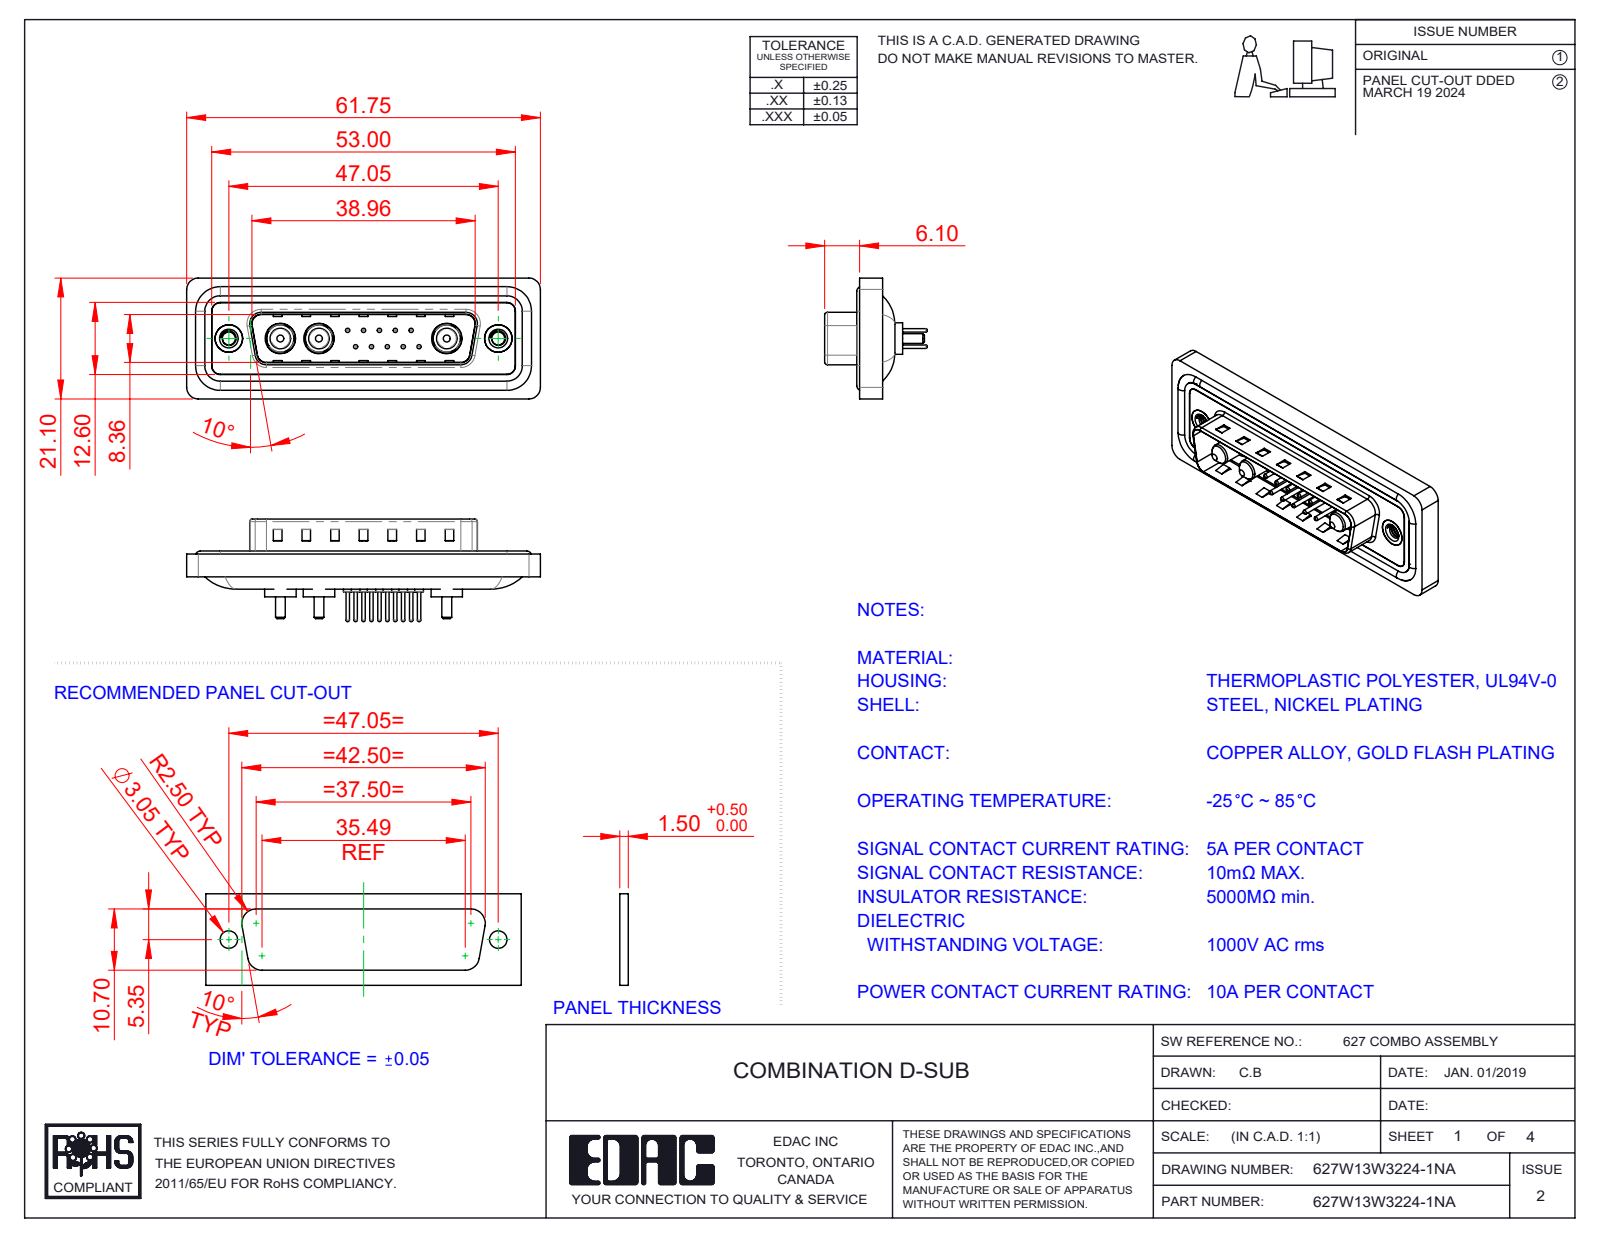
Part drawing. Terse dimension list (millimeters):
name: 627W13W3224-1NA; 627Combo Contact Row 1_24; 627Combo Shell Rear_25 Contacts; 627Combo Contact Row 2_24 (+5 more)
written by: SolidWorks 2023 (CONFIG_CONTROL_DESIGN)
unit: mm
bodies: 23 solids, 968 faces (309 planar, 387 cylindrical, 272 other)
size: 61.75 × 21.1 × 17.9
volume: 7 293 mm³; area: 11 834 mm²
holes: 10× ⌀0.75, 10× ⌀1.6, 10× ⌀2, 3× ⌀4.85, 3× ⌀5.3, 2× ⌀2.26, 2× ⌀4, 2× ⌀4.8, 2× ⌀5
bosses: 10× ⌀1.5, 10× ⌀0.6, 4× ⌀1.6, 3× ⌀5.5, 3× ⌀5.2, 3× ⌀4.75, 3× ⌀3.75, 3× ⌀3.6
rounds: 22× R1.5, 18× R2, 8× R0.5, 8× R1.6, 4× R0.25, 4× R0.6, 4× R0.65, 4× R0.9
face distances: 0.4, 1.5, 1.1, 1.6, 0.5, 3.1, 2.9, 0.82, 9.58, 4.1
hole spacings: 3.16, 2.77, 5.04, 5.54, 7.49, 5.03, 8.31, 10.11
